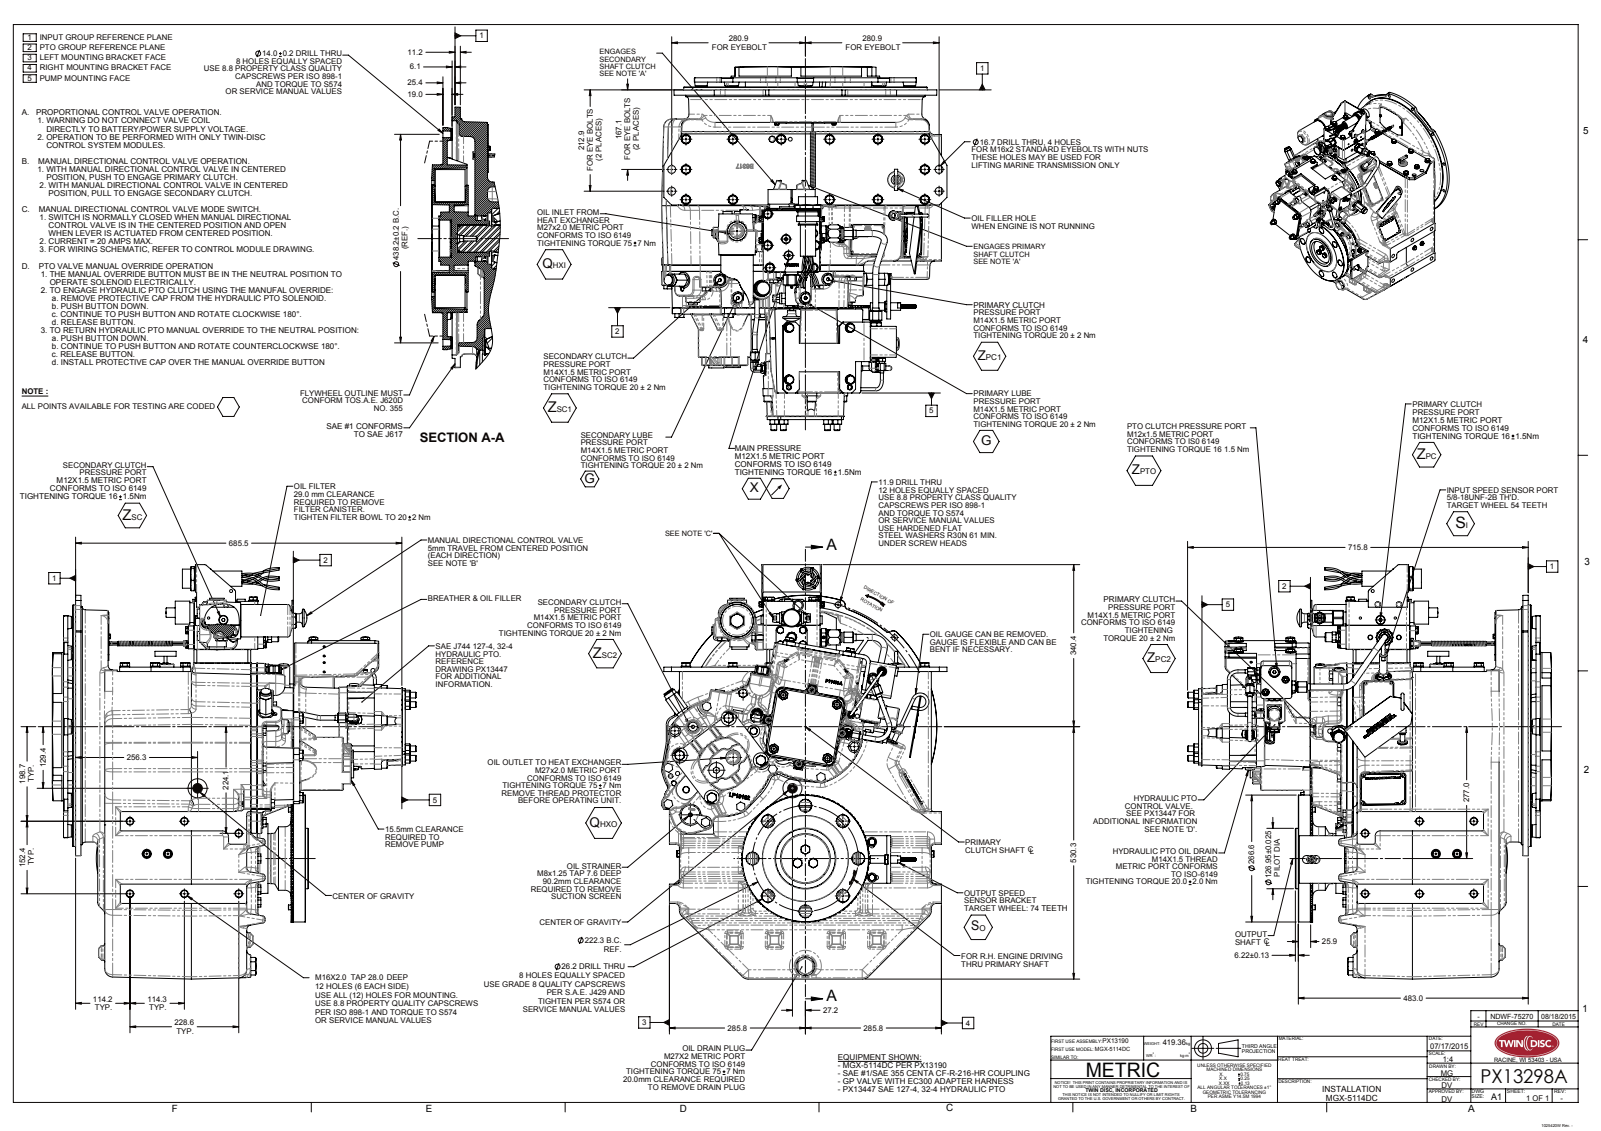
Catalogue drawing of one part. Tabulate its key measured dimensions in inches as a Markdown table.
| quantity | value |
| --- | --- |
| part name | PX13298A |
| STEP written by | SolidWorks 2010 (AUTOMOTIVE_DESIGN) |
| units | inches |
| bodies | 0 solids, 5717 faces (1899 planar, 1797 cylindrical, 2021 other) |
| overall size | 34.28 × 30.105 × 23.606 |
| round holes (diameter × count) | 0.469 × 12, 1.031 × 8, 0.165 × 7, 0.63 × 6, 0.346 × 4, 0.565 × 4, 0.656 × 4, 0.984 × 4, 0.189 × 3, 0.394 × 3, 0.748 × 3, 0.313 × 2 |
| round bosses / shafts (diameter × count) | 0.781 × 20, 0.748 × 12, 0.945 × 8, 0.75 × 8, 0.551 × 7, 0.472 × 7, 2.953 × 6, 0.787 × 6 |
| partial cylindrical surfaces (radius × count) | 1.808 × 91, 0.197 × 82, 0.079 × 76, 0.394 × 72, 0.059 × 70, 0.315 × 45, 0.098 × 33, 0.118 × 31 |
| main face-to-face distances | 12.607, 12.591, 0.017, 0.365, 0.867, 11.74, 0.851, 0.335, 12.075, 0.516 |
| hole center spacings | 10.437, 5.403, 10.437, 14.761, 18.078, 20.163, 4.375, 5.402 |
